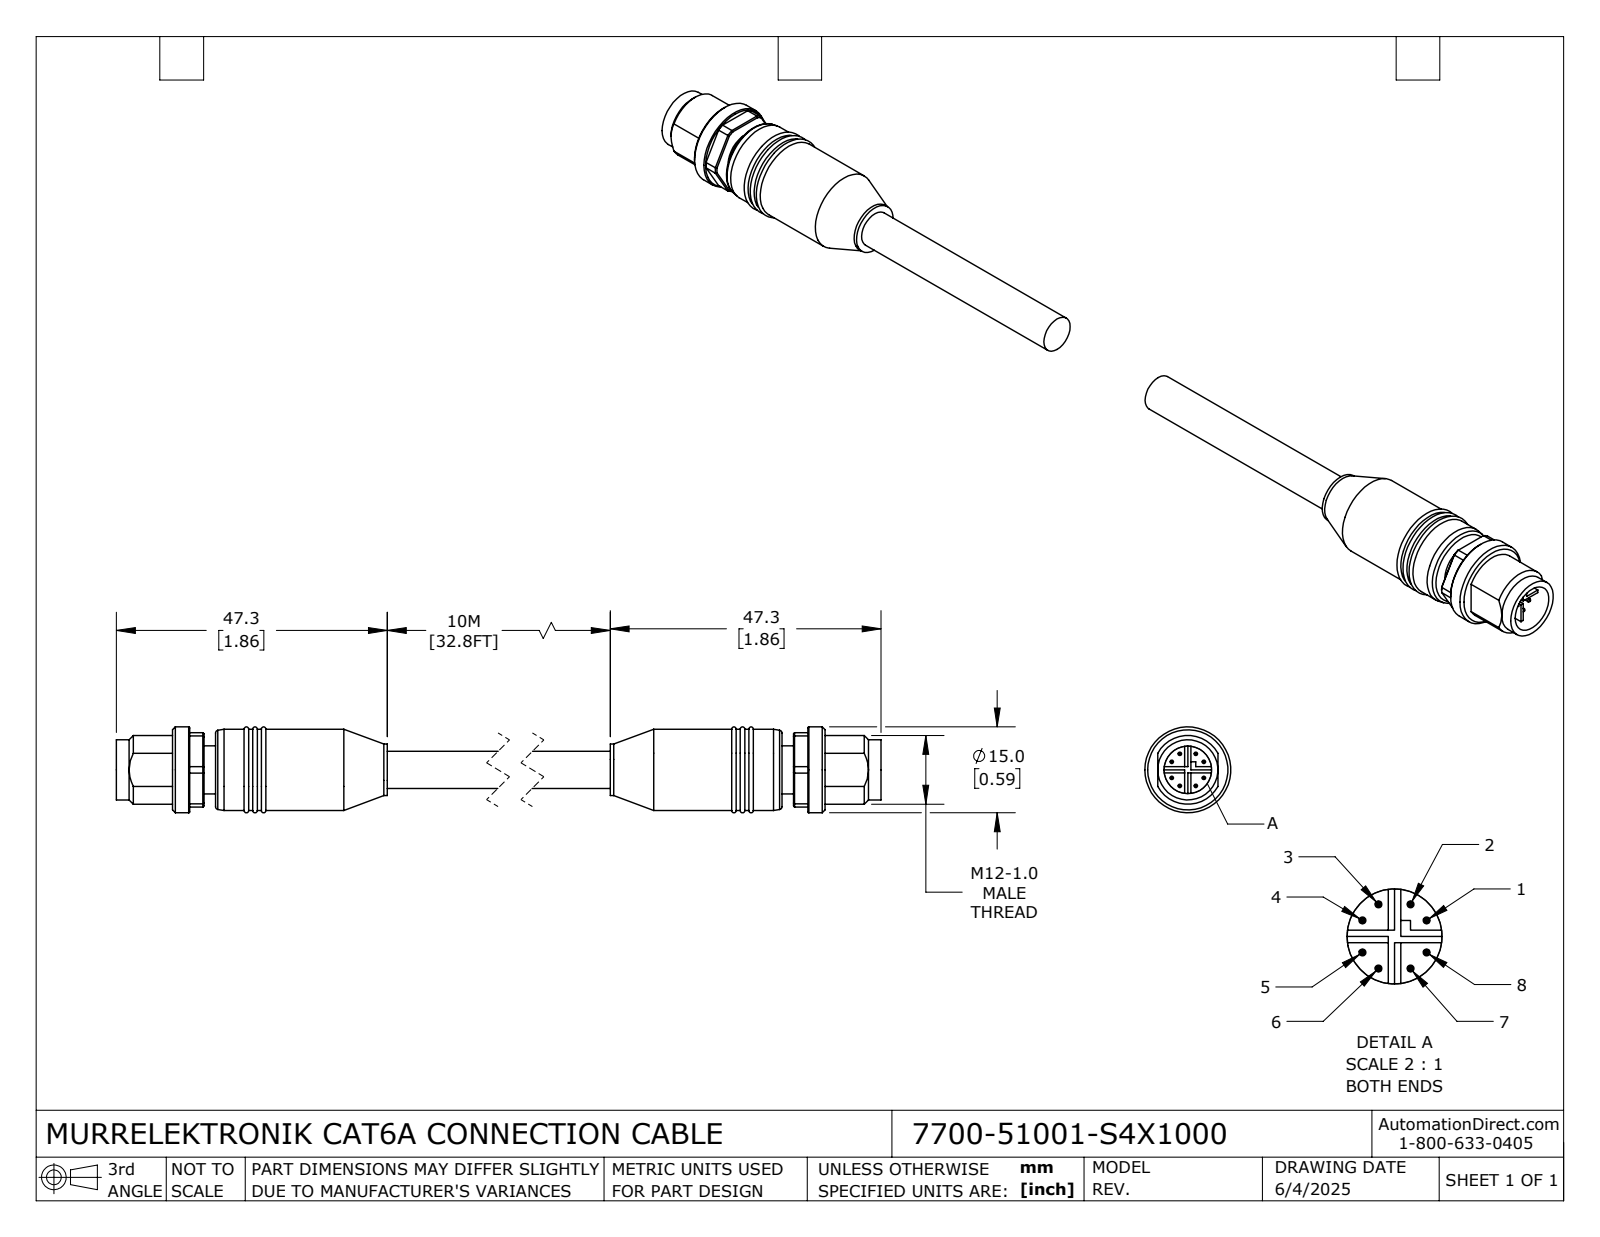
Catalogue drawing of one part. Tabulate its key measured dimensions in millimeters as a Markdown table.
| quantity | value |
| --- | --- |
| part name | 7700-51001-S4X1000; 7700-51001-S4X1000_MALE |
| STEP written by | SolidWorks 2024 (CONFIG_CONTROL_DESIGN) |
| units | millimeters |
| bodies | 2 solids, 282 faces (112 planar, 88 cylindrical, 82 other) |
| overall size | 209.6 × 15 × 15 |
| volume | 14 953 mm³ |
| surface area | 7 635 mm² |
| round holes (diameter × count) | 8.3 × 1 |
| round bosses / shafts (diameter × count) | 0.6 × 8, 15 × 1, 14.2 × 1, 10.5 × 1, 9 × 1, 8.4 × 1, 6.5 × 1 |
| partial cylindrical surfaces (radius × count) | 6 × 1, 7.2 × 1 |
| main face-to-face distances | 4.7, 5.8, 2, 177, 1.1, 5.5, 13, 7.5, 182.5, 184.5 |
